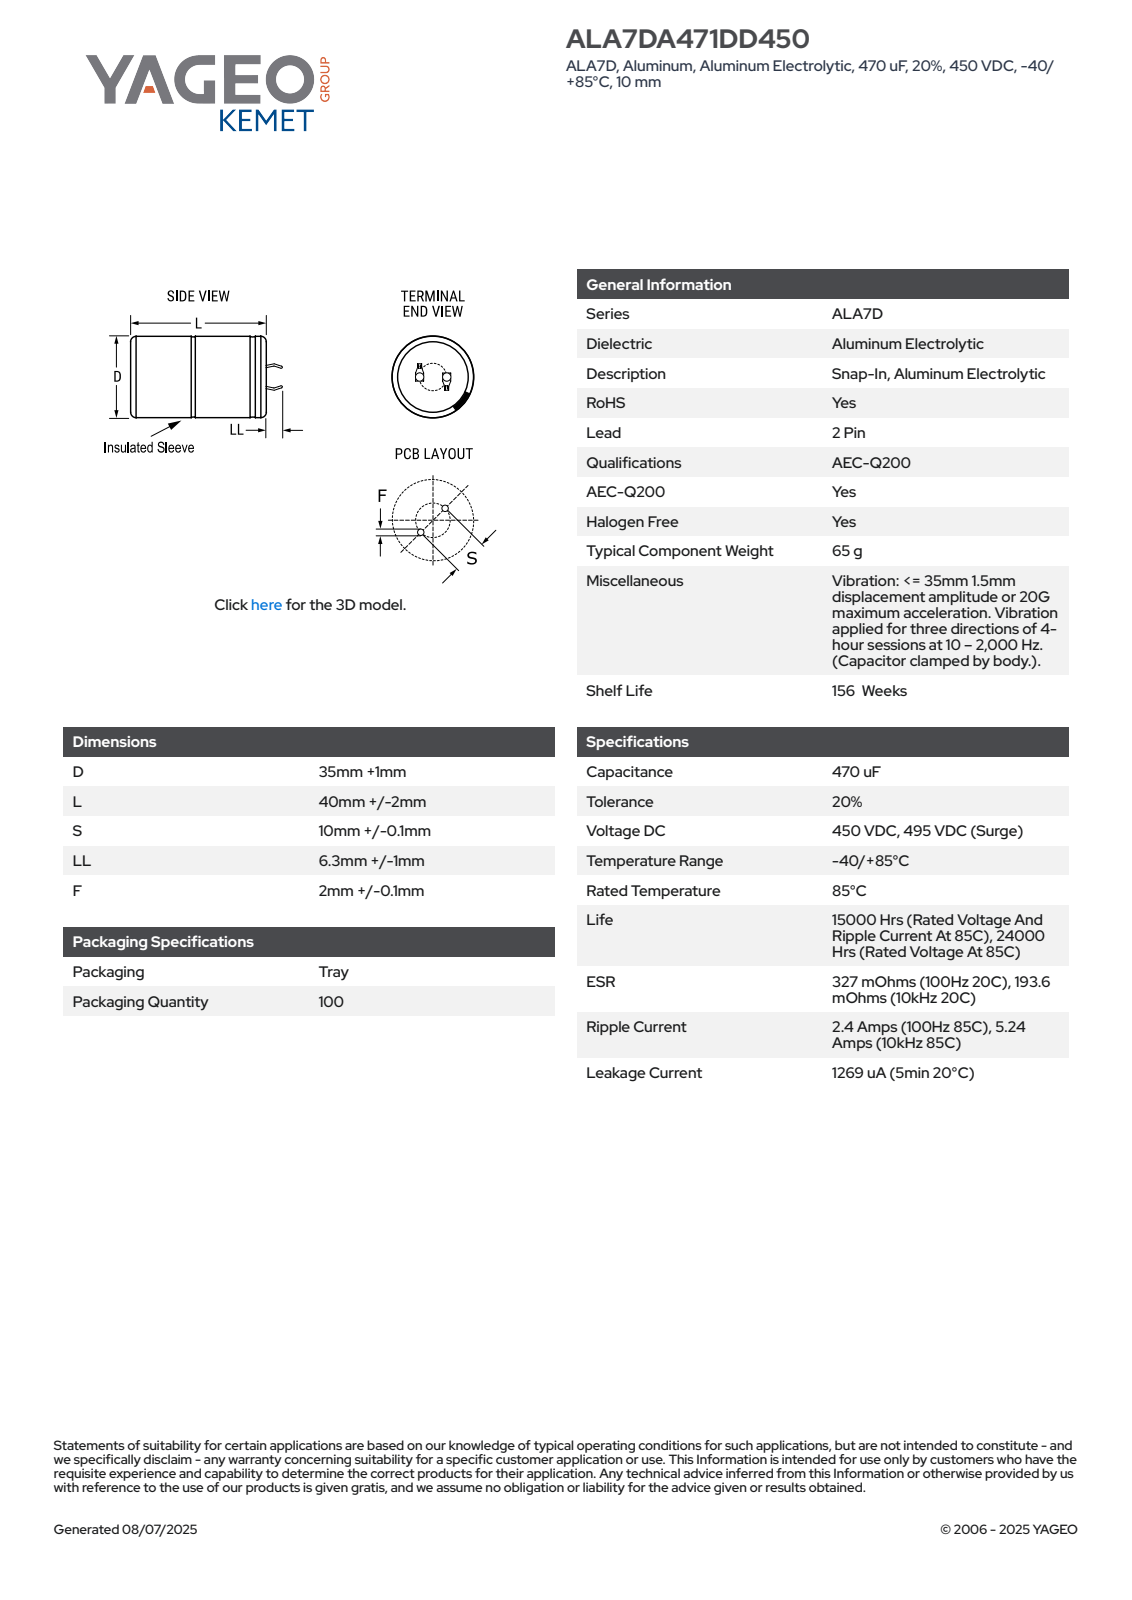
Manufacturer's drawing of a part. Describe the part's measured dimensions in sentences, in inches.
The part is named "CARS_K2PAV_35X40_D36L42S10LL7.3F2.1". Its 3-D file was written by "SolidWorks 2021 (AUTOMOTIVE_DESIGN)". It is 1 solid with 106 faces: 52 planar, 11 cylindrical and 43 other. Overall it measures 1.941 by 1.417 by 1.417 inches. Its volume is 2.574 cubic inches and its surface area 10.61 square inches. Round holes: 1 of diameter 1.254. Round bosses or shafts: 1 of diameter 1.417. Partial cylindrical surfaces (rounded edges, fillets, slot ends): 1 of radius 0.708. The main face-to-face distances are 1.653, 0.024, 1.673, 0.02, 0.279, 0.301, 0.053, 0.03, 0.302, 0.255.
